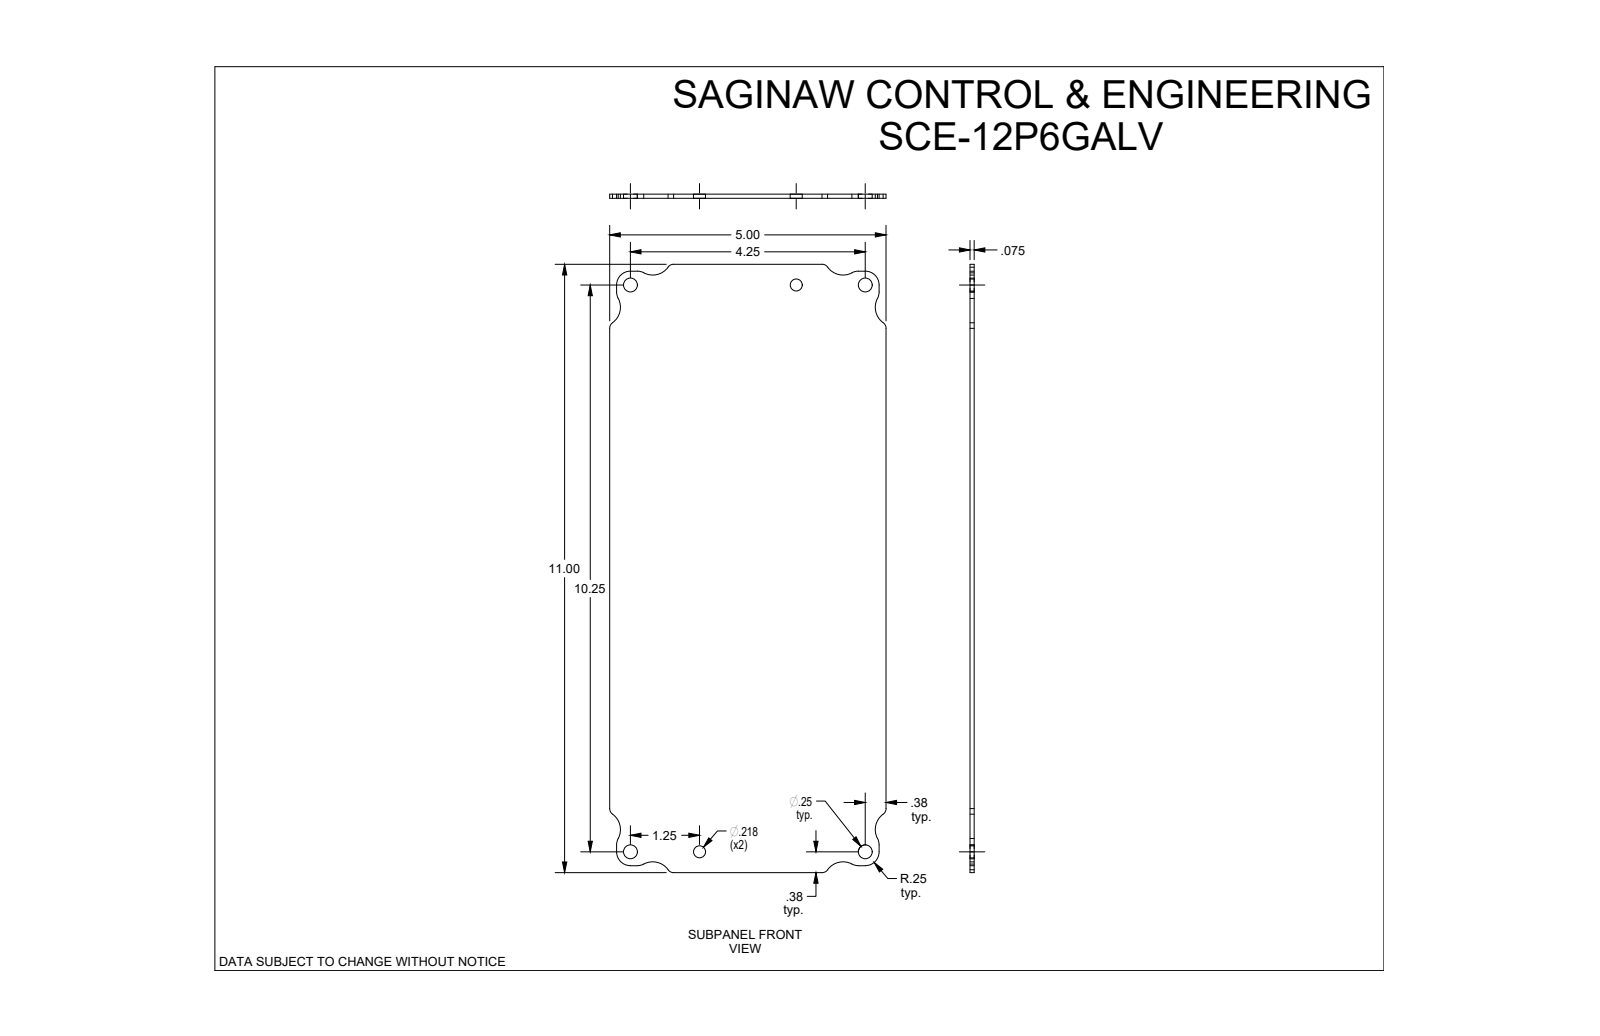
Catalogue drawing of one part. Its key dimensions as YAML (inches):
part_name: "SCE-12P6GALV"
step_written_by: "SolidWorks 2019 (CONFIG_CONTROL_DESIGN)"
units: inches
bodies: {solids: 1, faces: 48, planar: 14, cylindrical: 34, other: 0}
overall_size: [11, 5, 0.075]
volume: 4.015
surface_area: 109.7
round_holes:
  - {diameter: 0.25, count: 4}
  - {diameter: 0.218, count: 2}
partial_cylinders:
  - {radius: 0.25, count: 12}
  - {radius: 0.125, count: 8}
  - {radius: 0.344, count: 8}
face_to_face_distances: [0.075, 5, 11, 0.125, 10.875, 0.125, 4.875, 10.75, 4.75]
hole_center_spacings: [1.25, 3, 4.25, 10.25, 10.326, 10.68, 11.096, 10.398]
